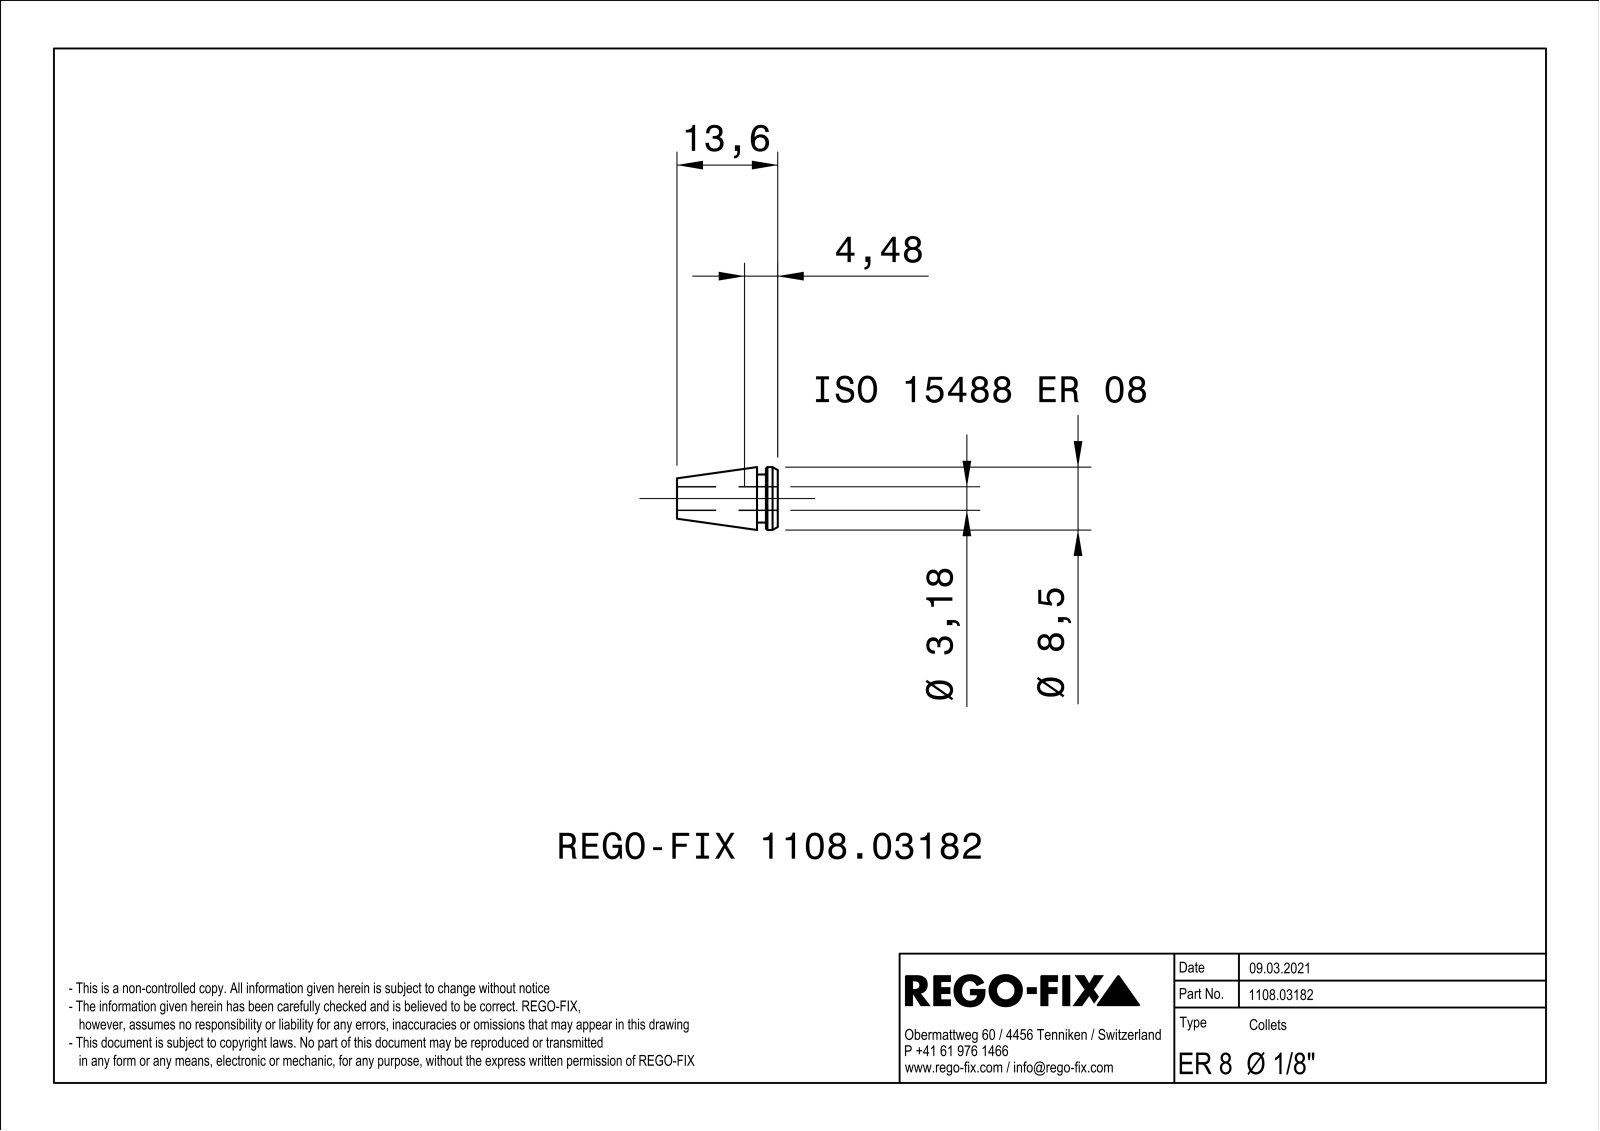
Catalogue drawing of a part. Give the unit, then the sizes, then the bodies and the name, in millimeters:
Units: millimetres
Overall size (bounding box): 13.6 × 8.49 × 8.49
Round holes (diameter × count): ⌀3.17 ×1
Round bosses / shafts (diameter × count): ⌀8.5 ×1, ⌀6.5 ×1
Partial cylindrical surfaces — rounded edges, fillets, slot ends (radius × count): R20 ×12
Main face-to-face distances: 0.4, 2.8, 1.6, 1.2, 13.6, 12, 10.8
Volume: 330 mm³ · Surface area: 969 mm²
Bodies: 1 solid, 211 faces (90 planar, 43 cylindrical, 78 other)
Part name (STEP PRODUCT): NOCUT
STEP written by: SIEMENS PLM Software Solid Edge ST10 (AUTOMOTIVE_DESIGN)
